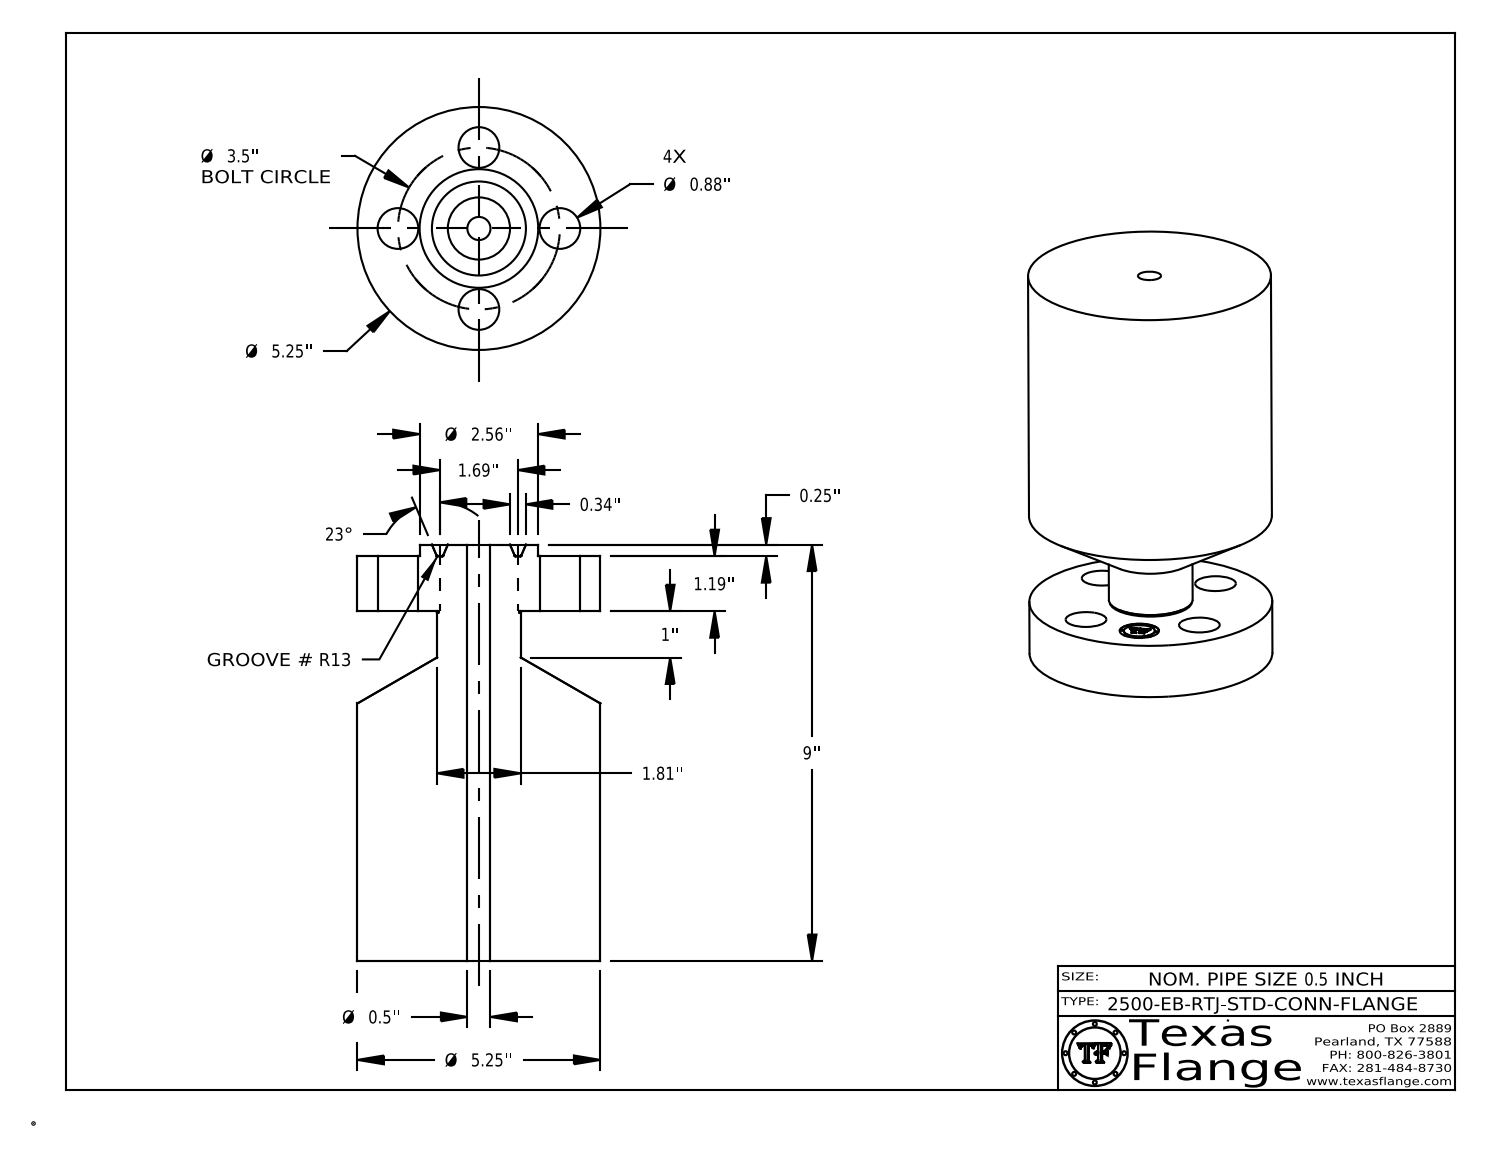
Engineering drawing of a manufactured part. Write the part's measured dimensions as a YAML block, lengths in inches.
part_name: "0.5-2500-EB-RTJ-STD-CONN-FLANGE"
step_written_by: "CATIA V5 STEP AP214 (AUTOMOTIVE_DESIGN)"
units: inches
bodies: {solids: 1, faces: 423, planar: 371, cylindrical: 38, other: 14}
overall_size: [9, 5.25, 5.25]
volume: 155.6
surface_area: 227.5
round_holes:
  - {diameter: 0.88, count: 4}
  - {diameter: 0.5, count: 1}
  - {diameter: 0.85, count: 1}
round_bosses_or_shafts:
  - {diameter: 0.051, count: 8}
  - {diameter: 5.25, count: 1}
  - {diameter: 2.563, count: 1}
  - {diameter: 1.81, count: 1}
  - {diameter: 0.67, count: 1}
face_to_face_distances: [7.56, 1.19, 8.75, 0.25, 1.44, 9, 1.435, 1.185, 7.565, 0.016]
hole_center_spacings: [1.75, 2.475, 1.339, 3.233, 3.5]
